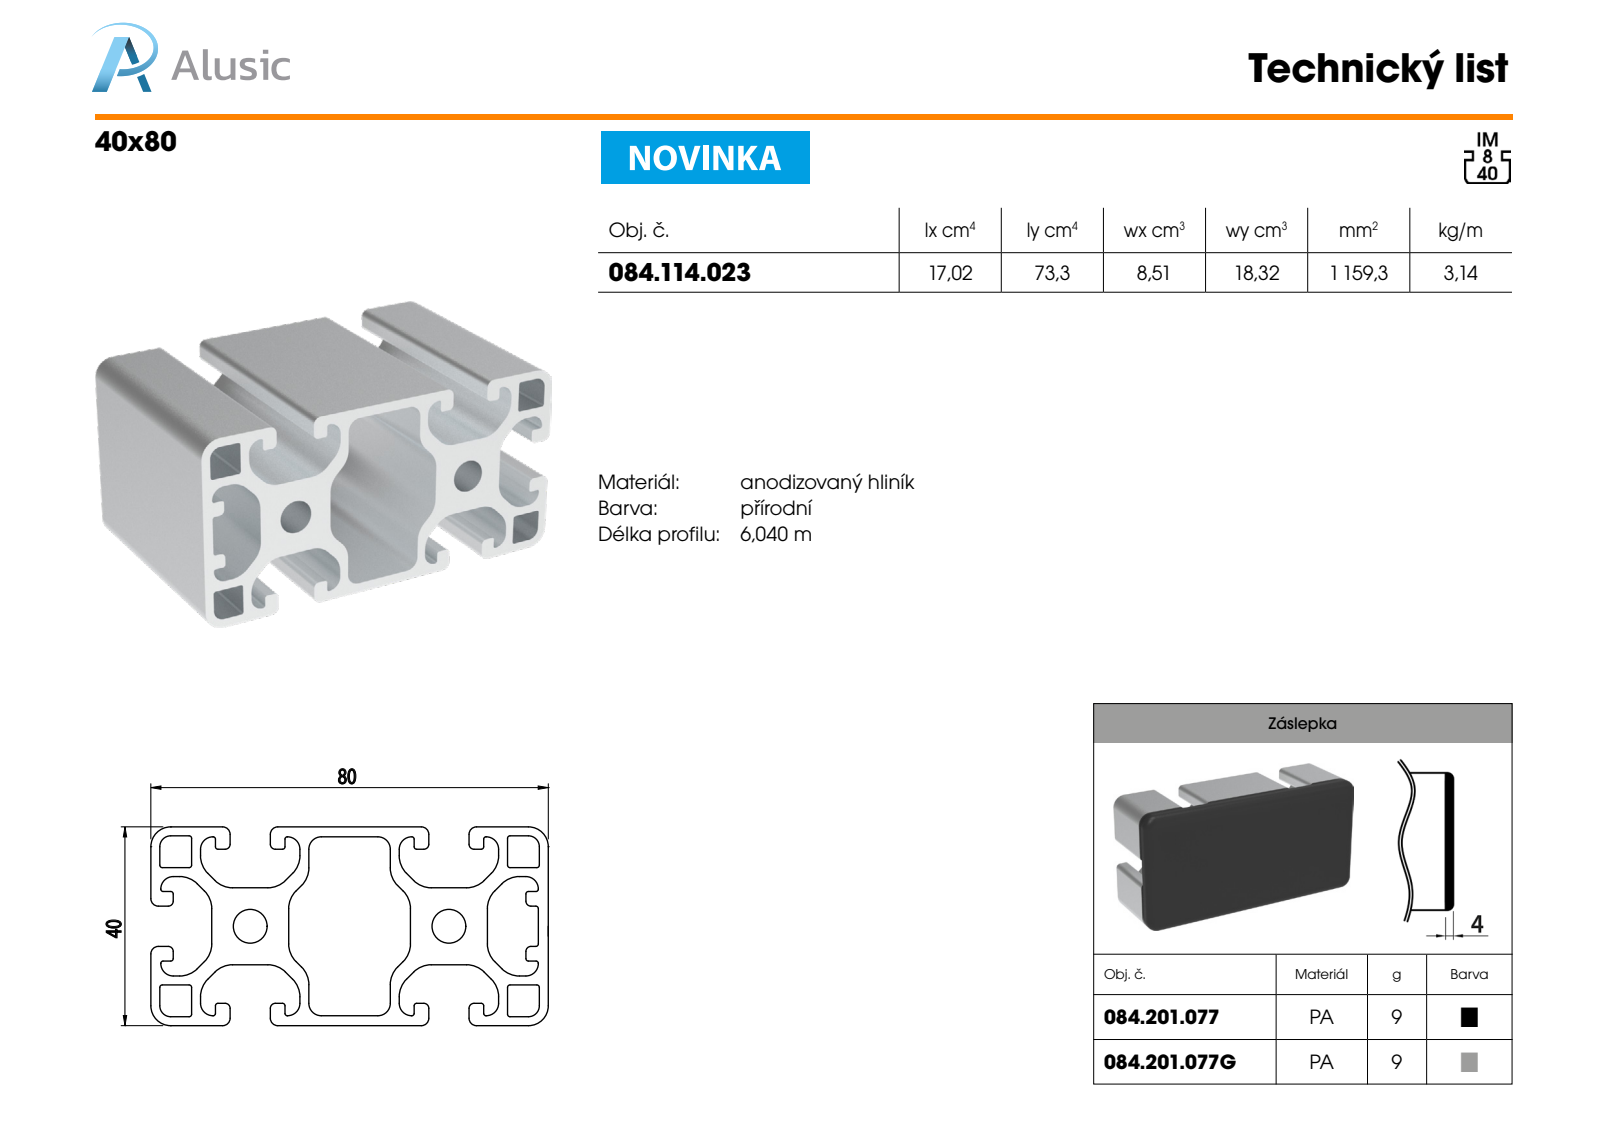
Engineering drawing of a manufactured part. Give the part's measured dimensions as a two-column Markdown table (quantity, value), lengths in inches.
| quantity | value |
| --- | --- |
| part name | 084.114.023 |
| STEP written by | SolidWorks 2018 (AUTOMOTIVE_DESIGN) |
| units | inches |
| bodies | 1 solid, 238 faces (117 planar, 121 cylindrical, 0 other) |
| overall size | 3.937 × 3.15 × 1.575 |
| volume | 7.074 in³ |
| surface area | 123.5 in² |
| round holes (diameter × count) | 0.268 × 2 |
| partial cylindrical surfaces (radius × count) | 0.197 × 32, 0.02 × 26, 0.098 × 16, 0.018 × 12, 0.039 × 12, 0.059 × 10, 0.087 × 4, 0.157 × 4 |
| main face-to-face distances | 1.575, 0.77, 0.159, 0.323, 1.093, 0.482, 1.252, 0.071, 1.181, 0.305 |
| hole center spacings | 1.575 |
